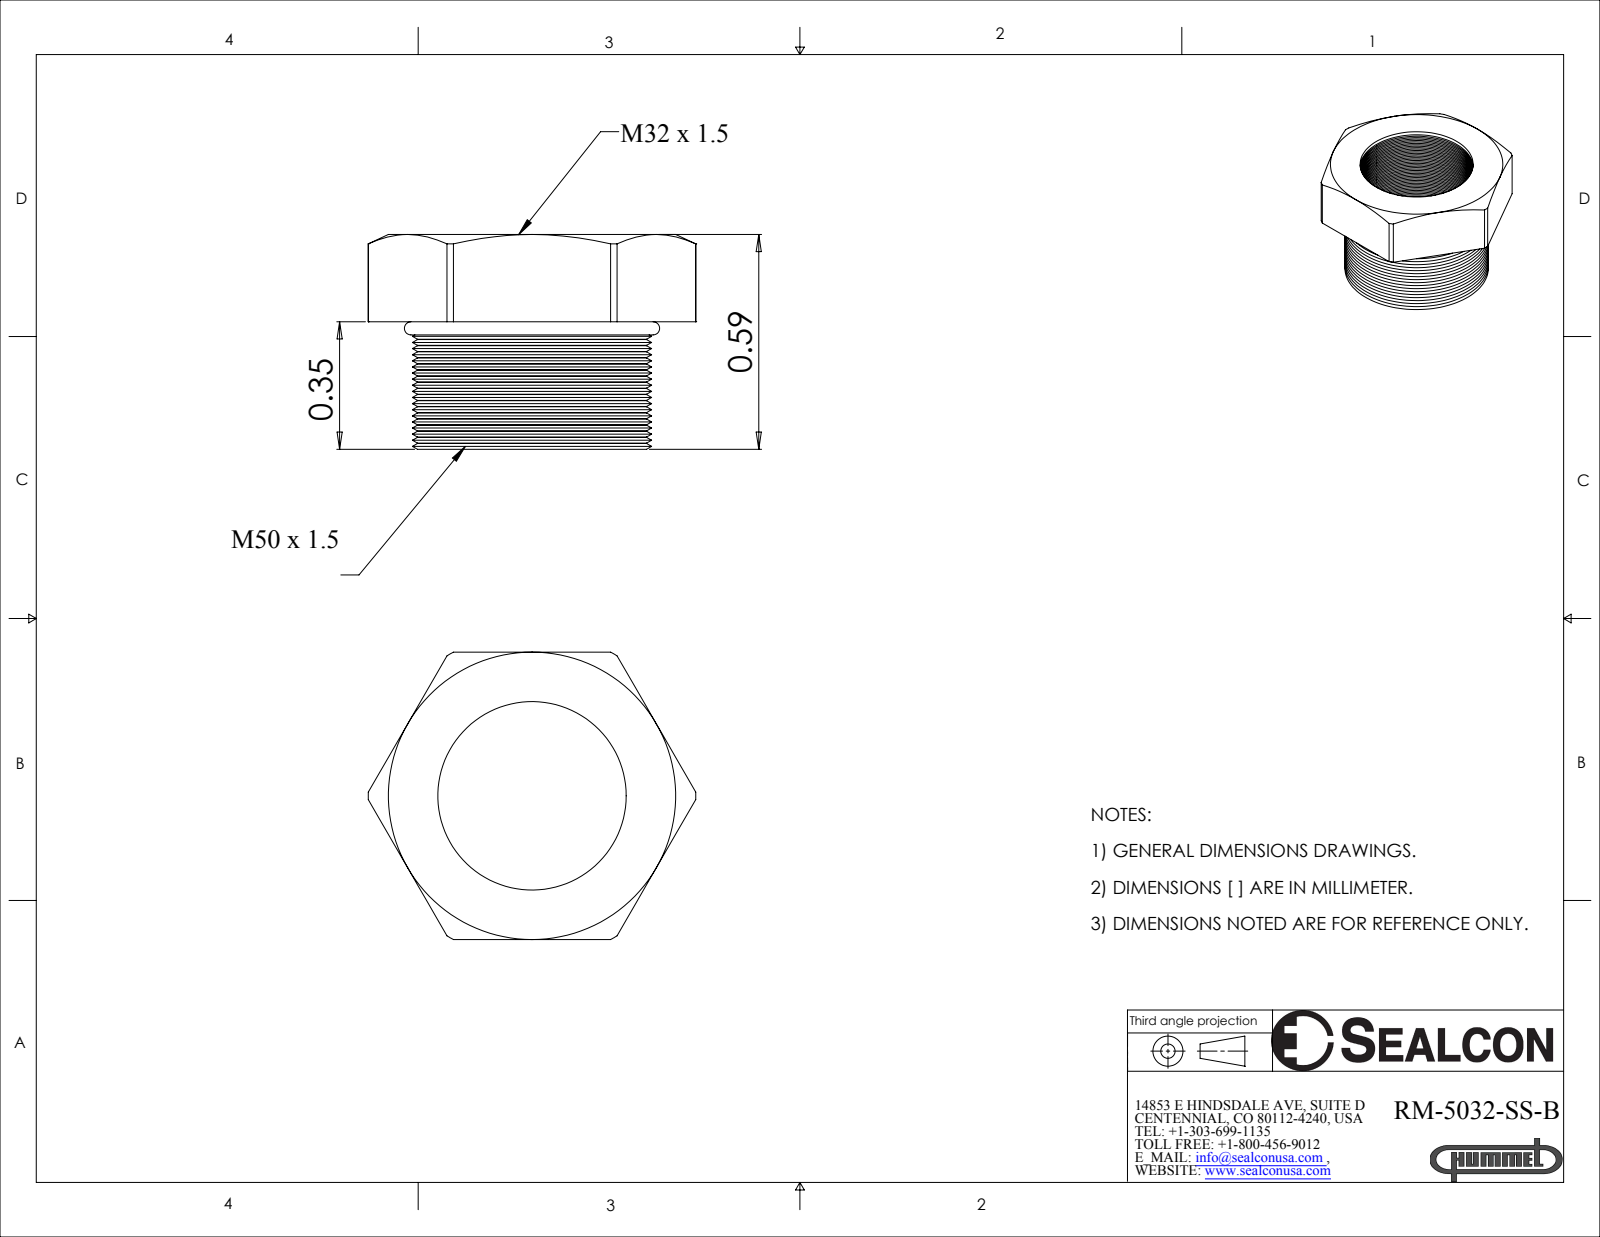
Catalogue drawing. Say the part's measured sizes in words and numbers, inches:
The part is named "RM-5032-SS-B". Its 3-D file was written by "SolidWorks 2008 (CONFIG_CONTROL_DESIGN)". It is 2 solids with 361 faces: 9 planar, 121 cylindrical and 231 other. Overall it measures 0.901 by 0.79 by 0.59 inches. Its volume is 0.118 cubic inches and its surface area 4.79 square inches. Round holes: 1 of diameter 0.518. Round bosses or shafts: 1 of diameter 0.63. Partial cylindrical surfaces (rounded edges, fillets, slot ends): 1 of radius 0.45. The main face-to-face distances are 0.79, 0.24, 0.35, 0.59.
